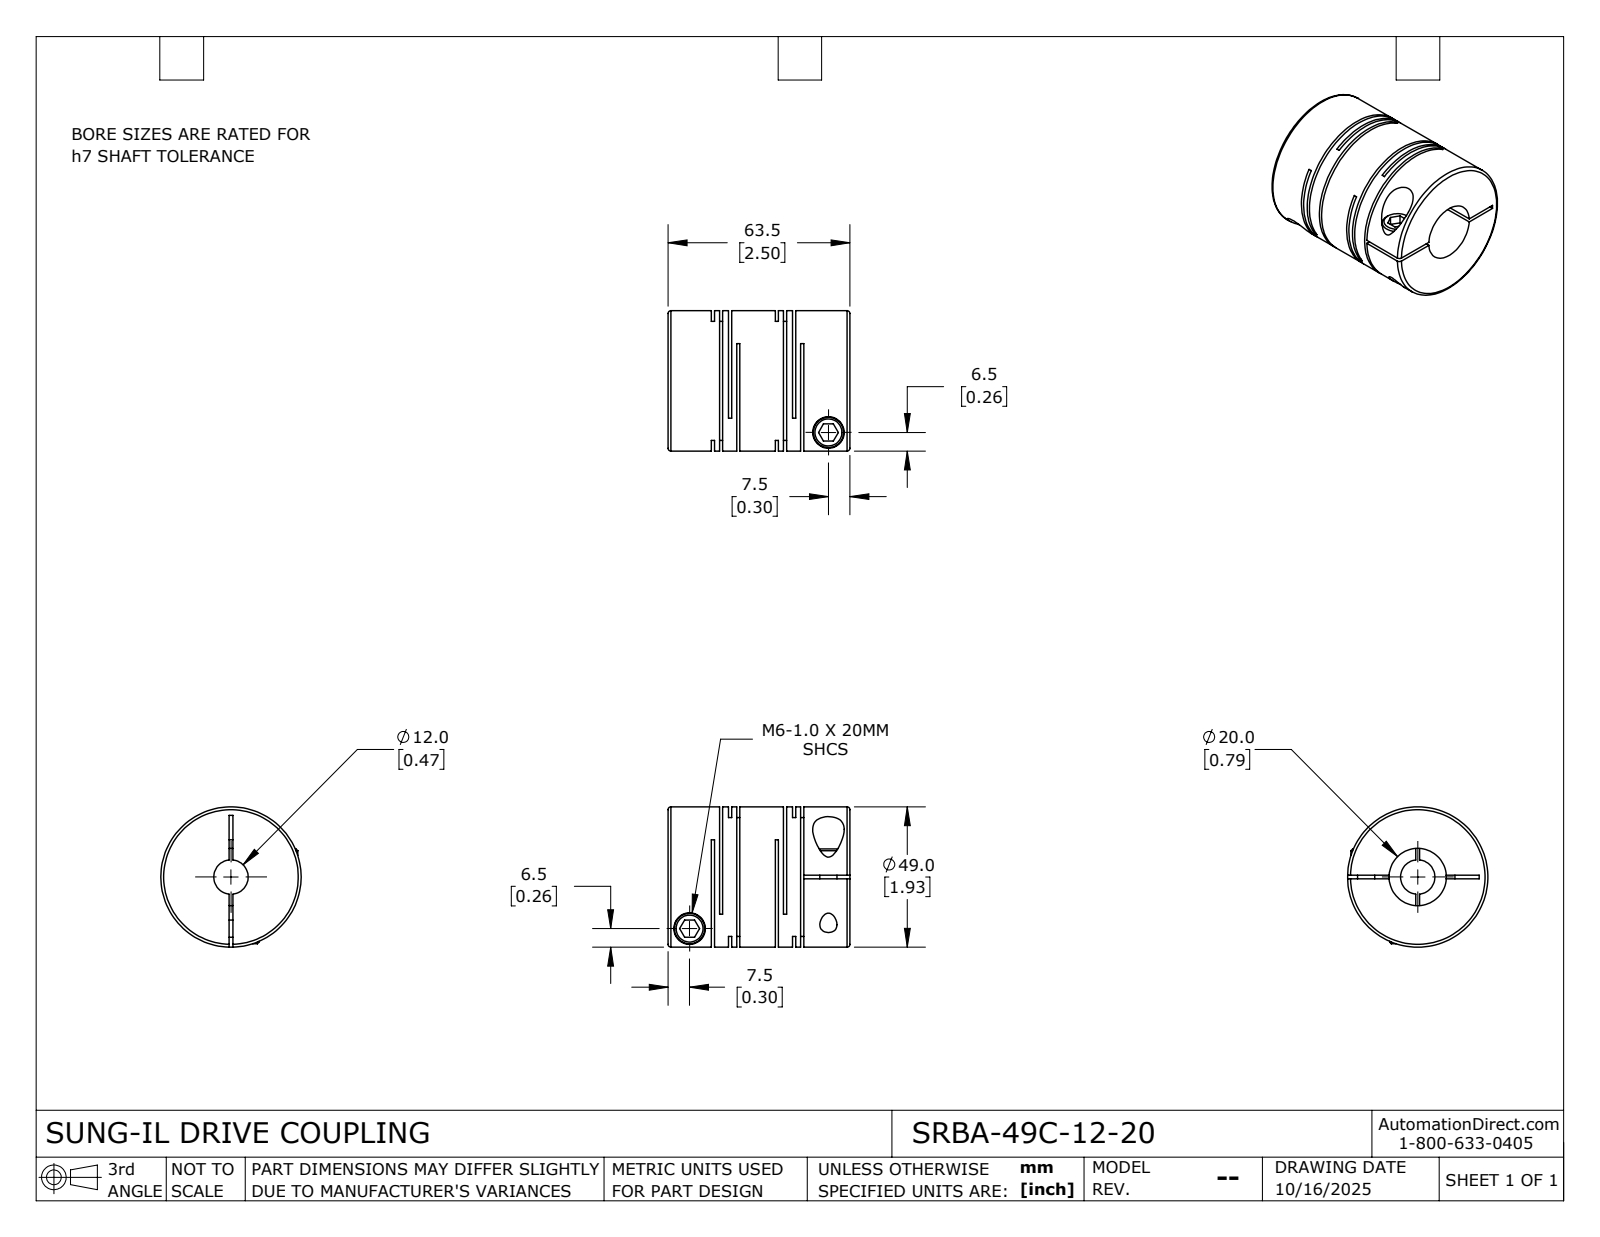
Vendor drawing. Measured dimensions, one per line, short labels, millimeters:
name: SRBA-49C-12-20
written by: SolidWorks 2024 (CONFIG_CONTROL_DESIGN)
unit: mm
bodies: 1 solid, 115 faces (60 planar, 42 cylindrical, 13 other)
size: 63.5 × 49 × 49
volume: 89 088 mm³; area: 38 219 mm²
holes: 2× ⌀6, 2× ⌀11, 1× ⌀12, 1× ⌀20
bosses: 2× ⌀10.6, 1× ⌀49
face distances: 6, 1.1, 22.35, 2.85, 21.25, 3.15, 1.75, 4.9, 19.5, 16.35
